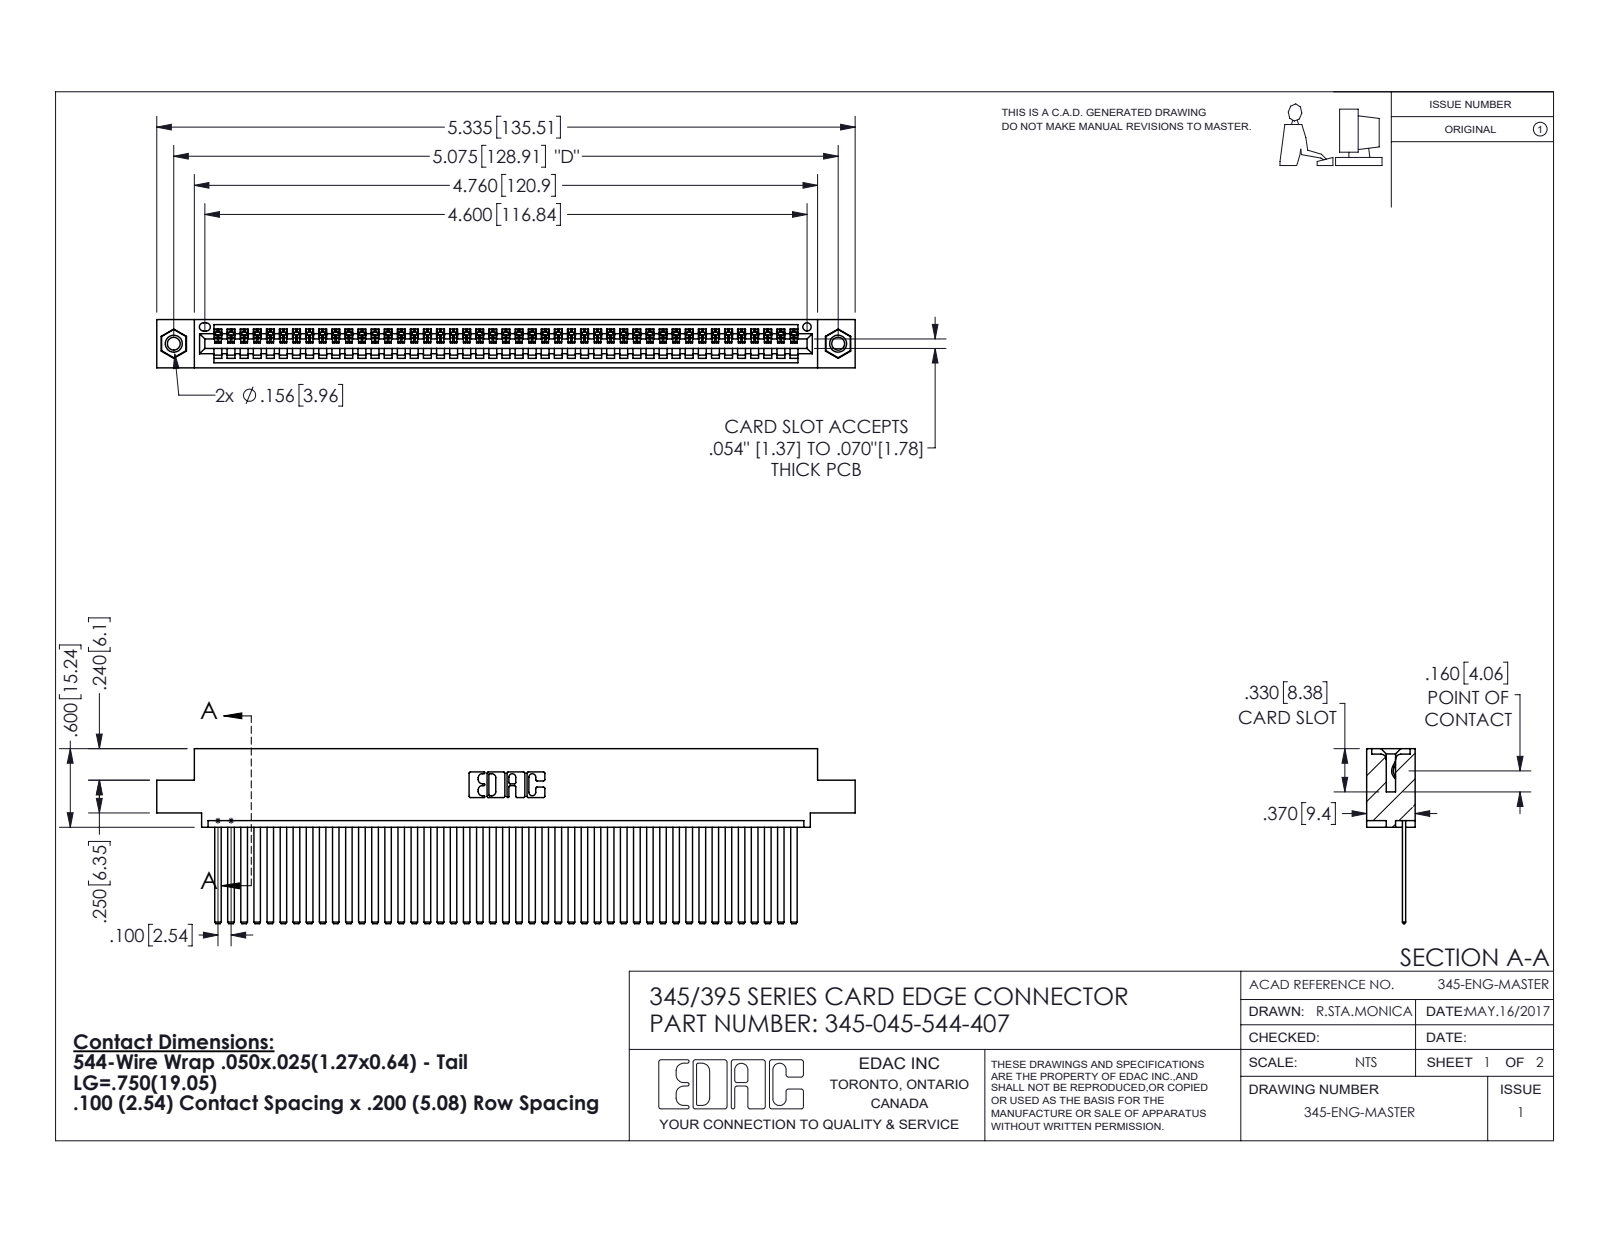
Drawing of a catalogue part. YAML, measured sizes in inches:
part_name: "345-045-544-407; 345-250-001_345-250-005-103; 345 Part_0.110 Offset - 0.156 Dia-TI; 345-292-001_345-293-144"
step_written_by: "SolidWorks 2016 (CONFIG_CONTROL_DESIGN)"
units: inches
bodies: {solids: 48, faces: 2530, planar: 1736, cylindrical: 778, other: 16}
overall_size: [5.335, 1.337, 0.37]
volume: 0.813
surface_area: 30.12
round_holes:
  - {diameter: 0.098, count: 2}
  - {diameter: 0.125, count: 2}
  - {diameter: 0.156, count: 2}
  - {diameter: 0.064, count: 1}
round_bosses_or_shafts:
  - {diameter: 0.155, count: 2}
partial_cylinders:
  - {radius: 0.006, count: 90}
  - {radius: 0.01, count: 22}
  - {radius: 0.007, count: 6}
  - {radius: 0.031, count: 6}
  - {radius: 0.026, count: 3}
  - {radius: 0.031, count: 2}
  - {radius: 0.04, count: 2}
  - {radius: 0.014, count: 1}
face_to_face_distances: [0.072, 0.298, 0.025, 0.098, 0.272, 0.37, 0.2, 0.225, 0.149, 0.072]
hole_center_spacings: [0.27, 4.839, 5.075]
